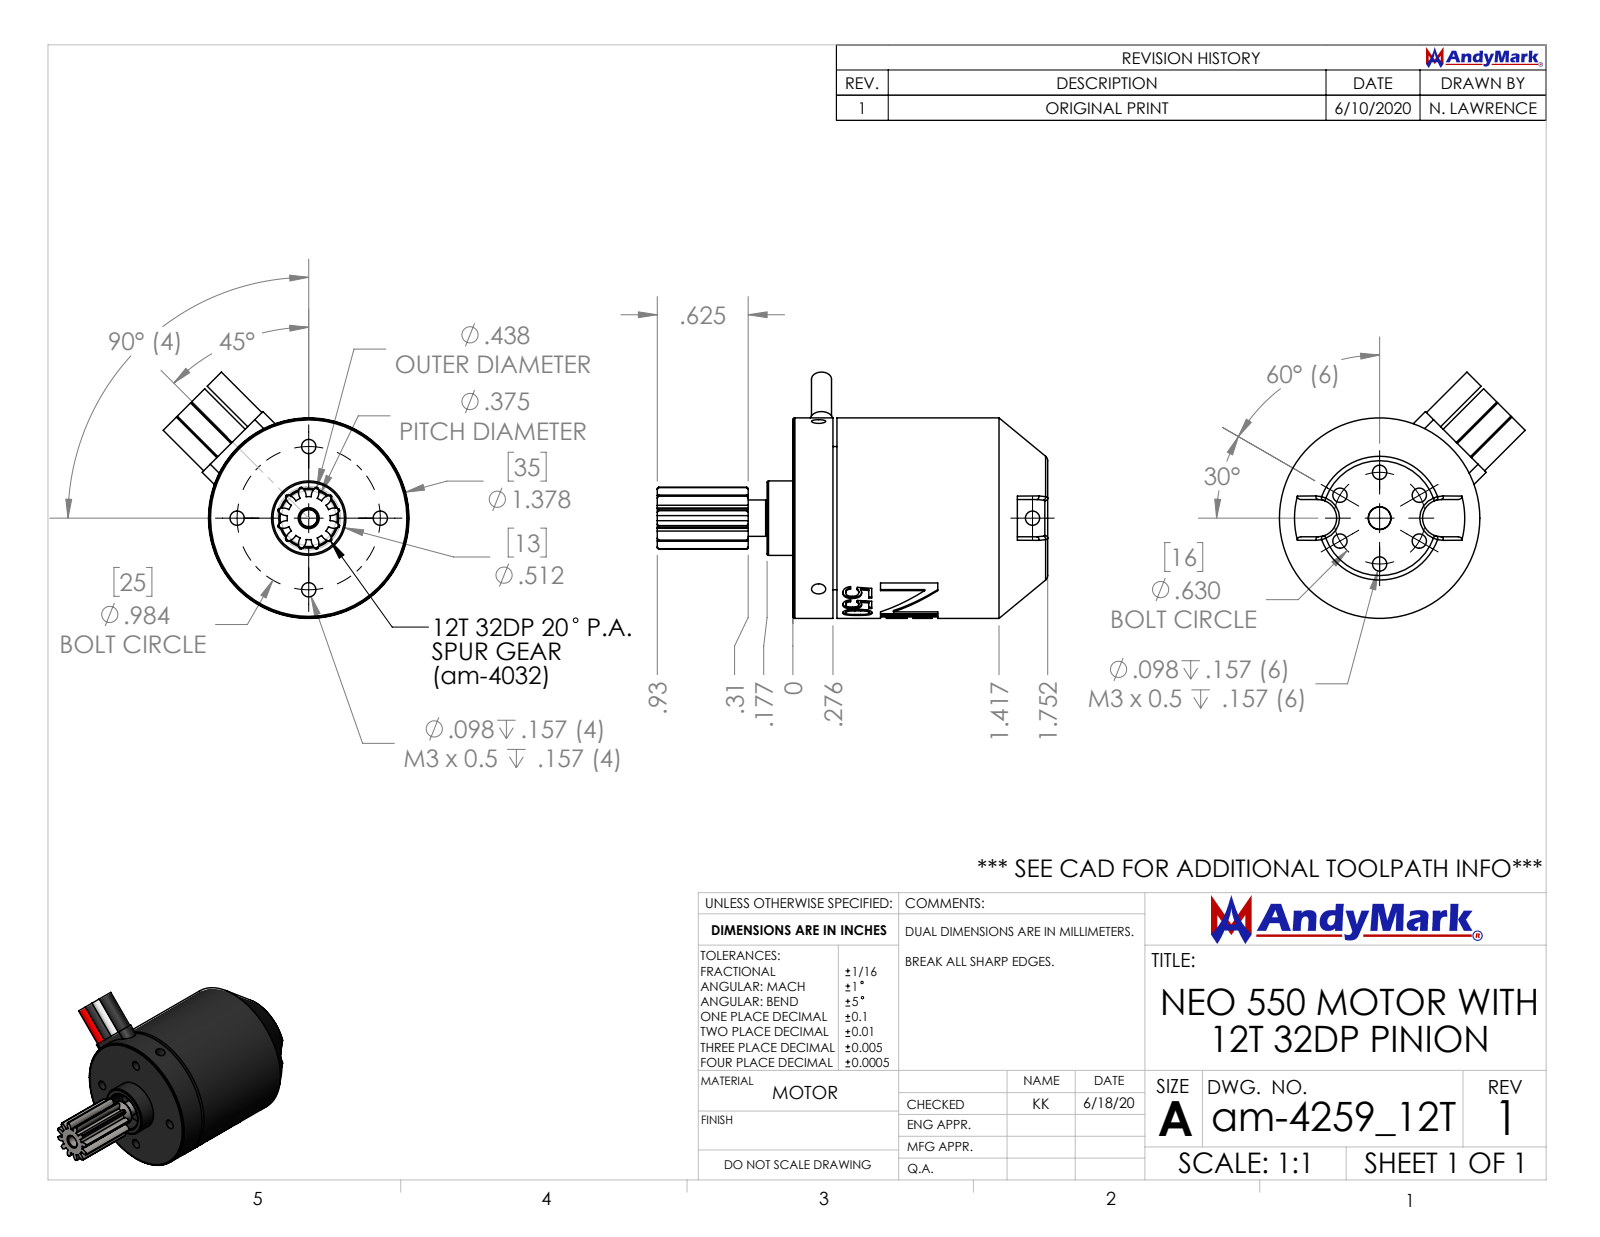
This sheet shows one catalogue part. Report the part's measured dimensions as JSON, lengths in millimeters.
{"part_name": "am-4259_12T NEO550 with 12T 32DP Pinion", "step_written_by": "SolidWorks 2019 (AUTOMOTIVE_DESIGN)", "units": "millimeters", "bodies": {"solids": 2, "faces": 255, "planar": 64, "cylindrical": 89, "other": 102}, "overall_size": [68.18, 43, 42.91], "volume_mm3": 40758, "surface_area_mm2": 10107, "round_holes": [[2.5, 14], [3.17, 1], [4, 1], [10, 1]], "round_bosses_or_shafts": [[3.25, 3], [35, 1], [25, 1], [13, 1], [6.35, 1], [3.9, 1], [3.5, 1], [3.17, 1]], "partial_cylinders_radius": [[1.91, 24], [2, 2], [3.25, 2], [3.76, 1], [5.56, 1], [17.25, 1]], "face_to_face_distances": [7, 0.7, 7.7, 36.8, 37.5, 44.5, 5.3, 31.5, 32.2, 39.2], "hole_center_spacings": [8, 13.86, 6.86, 10.97, 12.5, 14.84, 17.68, 17.9]}
